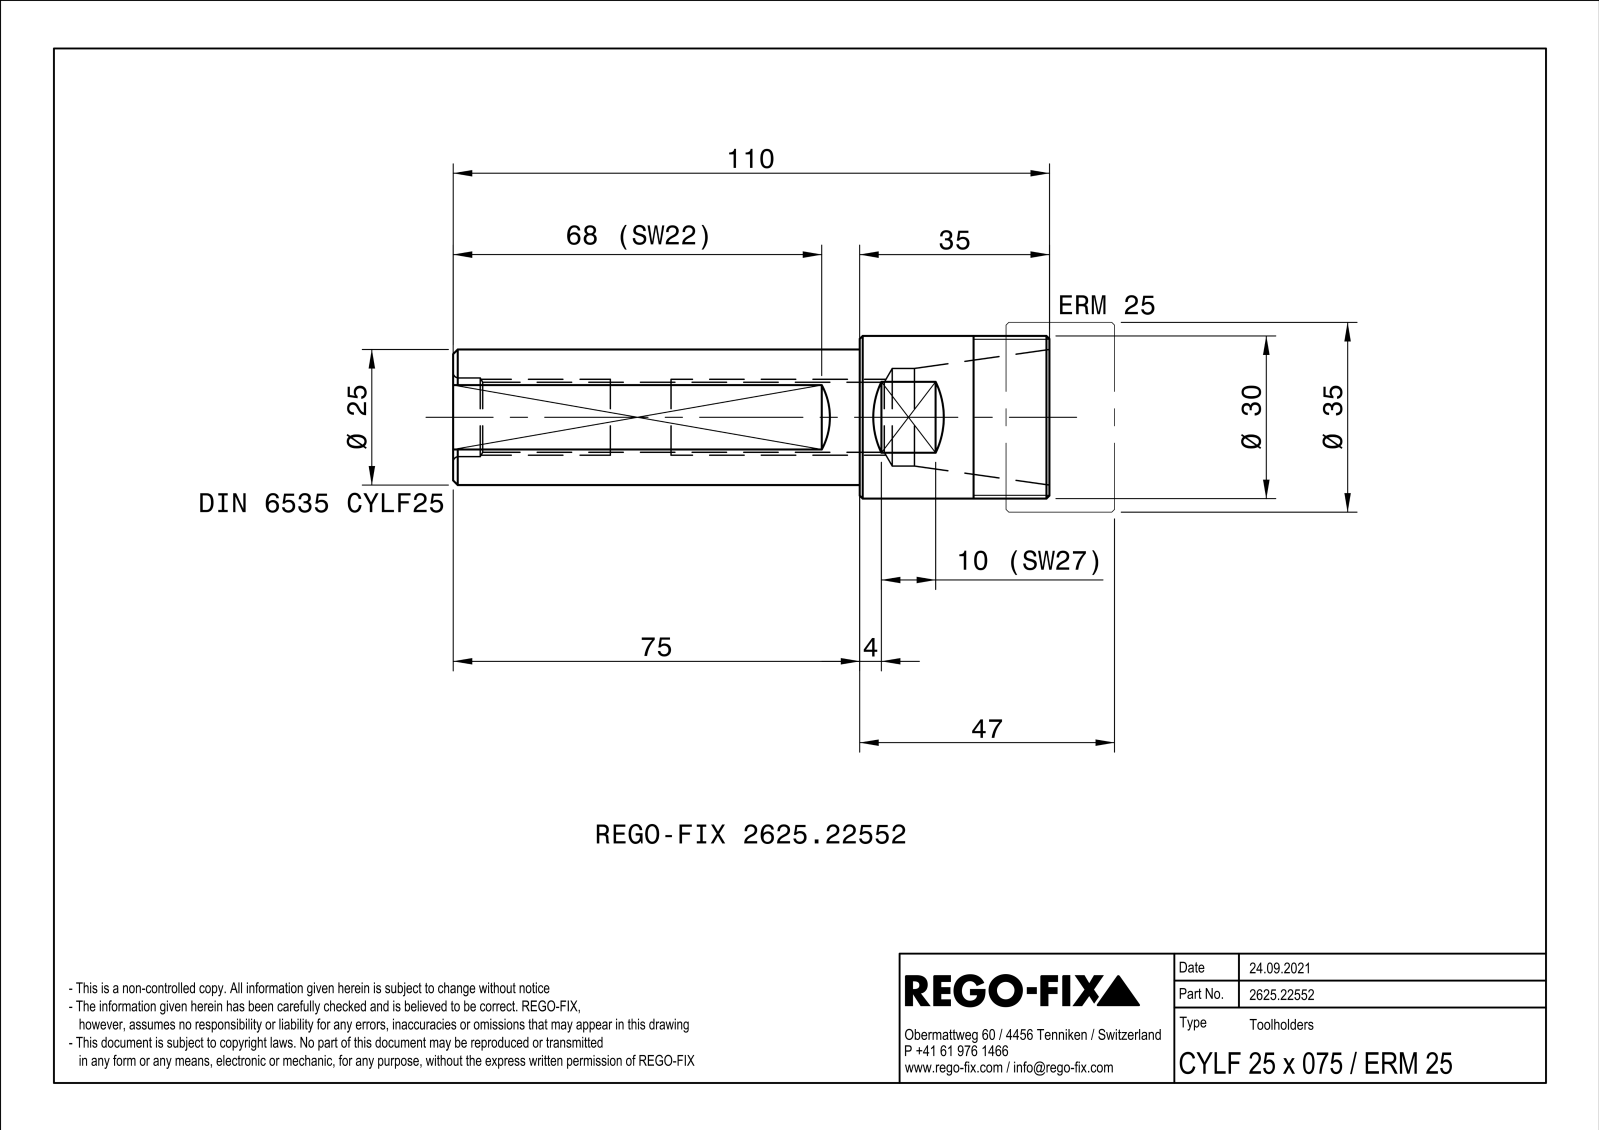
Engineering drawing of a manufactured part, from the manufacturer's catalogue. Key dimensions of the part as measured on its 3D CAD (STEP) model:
Part name (STEP PRODUCT): NOCUT
STEP written by: SIEMENS PLM Software Solid Edge ST10 (AUTOMOTIVE_DESIGN)
Units: millimetres
Bodies: 1 solid, 31 faces (12 planar, 9 cylindrical, 10 other)
Overall size (bounding box): 110 × 30 × 30
Volume: 39 307 mm³ · Surface area: 15 132 mm²
Round holes (diameter × count): ⌀12.92 ×1, ⌀14.5 ×1, ⌀18 ×1
Round bosses / shafts (diameter × count): ⌀30 ×1, ⌀25 ×1, ⌀24.6 ×1
Main face-to-face distances: 110, 35, 75, 24.5, 27, 2.5, 12.02, 25.09, 13.07, 72.57
